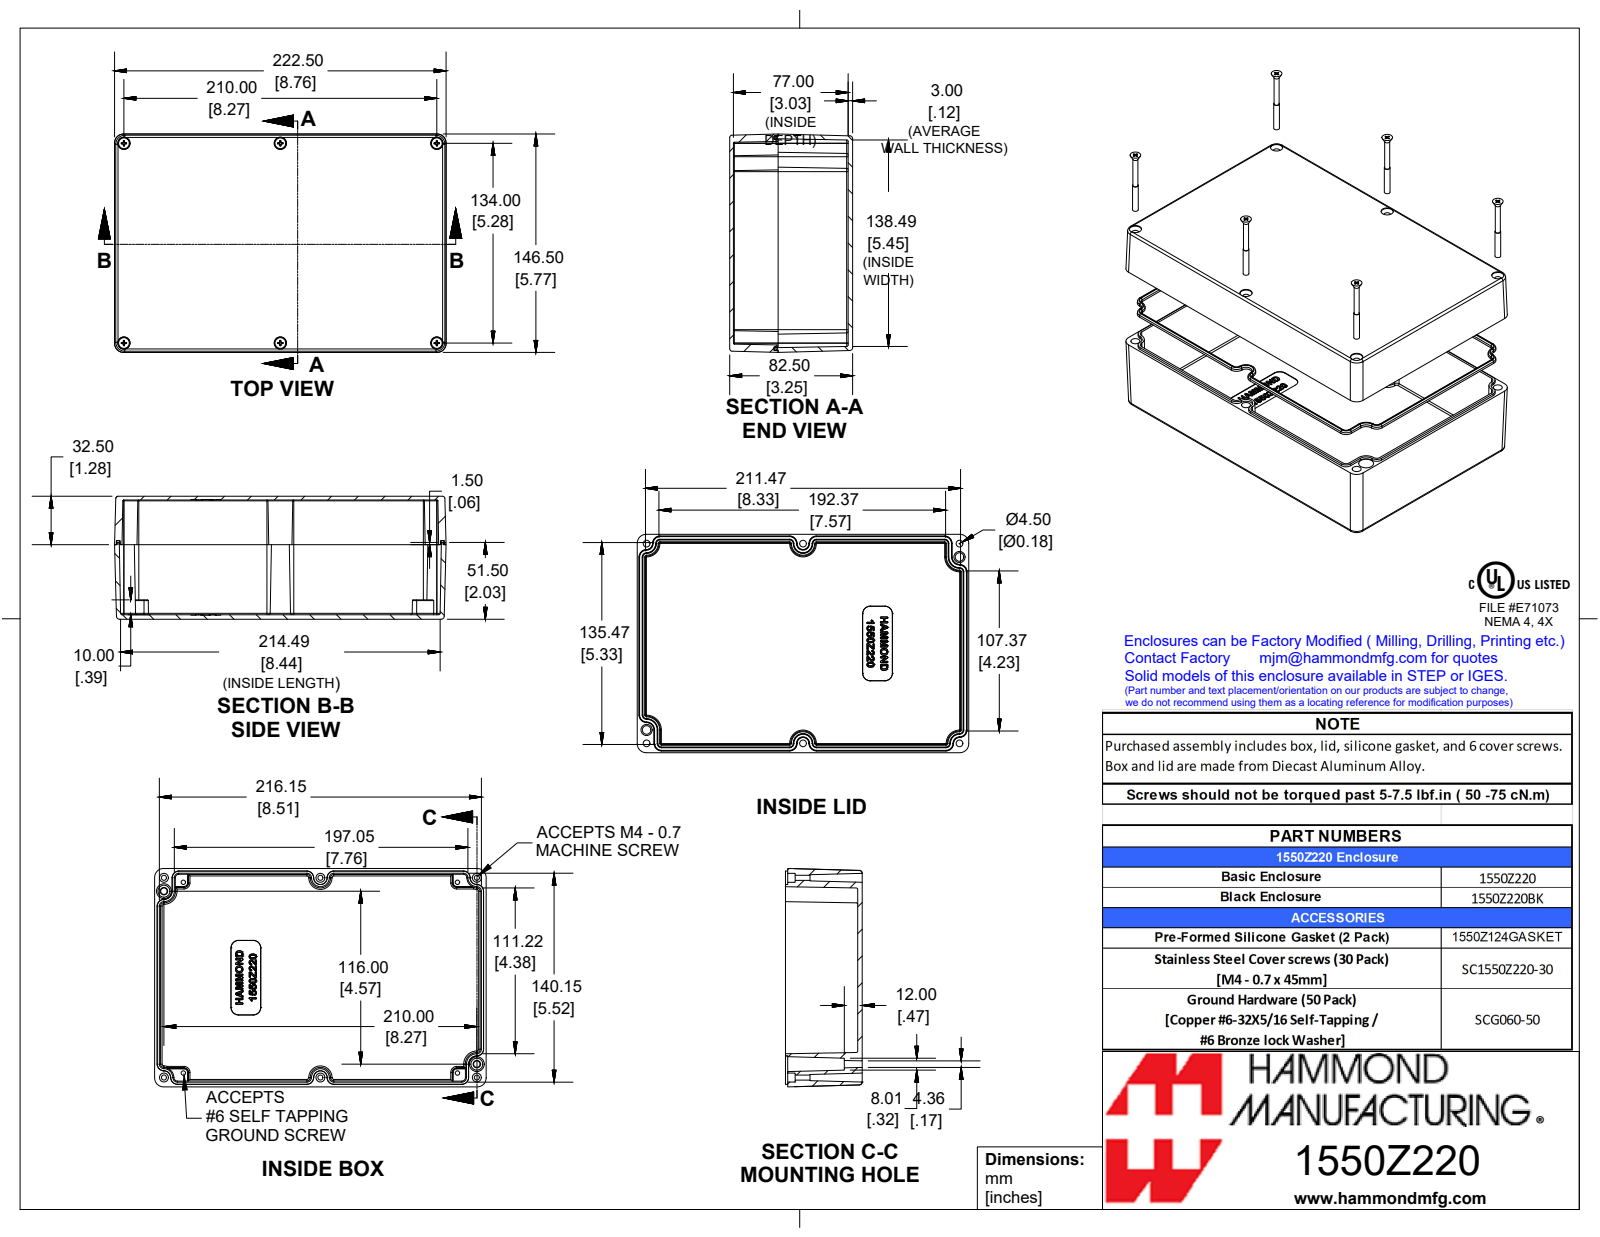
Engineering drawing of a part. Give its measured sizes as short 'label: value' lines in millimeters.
name: 1550Z220
written by: SolidWorks 2019 (AUTOMOTIVE_DESIGN)
unit: mm
bodies: 13 solids, 1908 faces (538 planar, 354 cylindrical, 1016 other)
size: 222.5 × 146.5 × 82.5
volume: 423 900 mm³; area: 268 100 mm²
holes: 6× ⌀3.4, 6× ⌀4.5, 6× ⌀6, 4× ⌀3
bosses: 6× ⌀7.5, 6× ⌀3.9, 6× ⌀3.3, 4× ⌀7, 4× ⌀3.5
rounds: 44× R1, 28× R0.3, 14× R0.6, 8× R6, 4× R0.5, 4× R1.5, 4× R2
face distances: 82.5, 3, 79.5, 80, 77, 2.5, 146.5, 138.3, 222.5, 214.3
hole spacings: 13.3, 92, 105, 131.6, 160.1, 170.2, 197, 236.6
